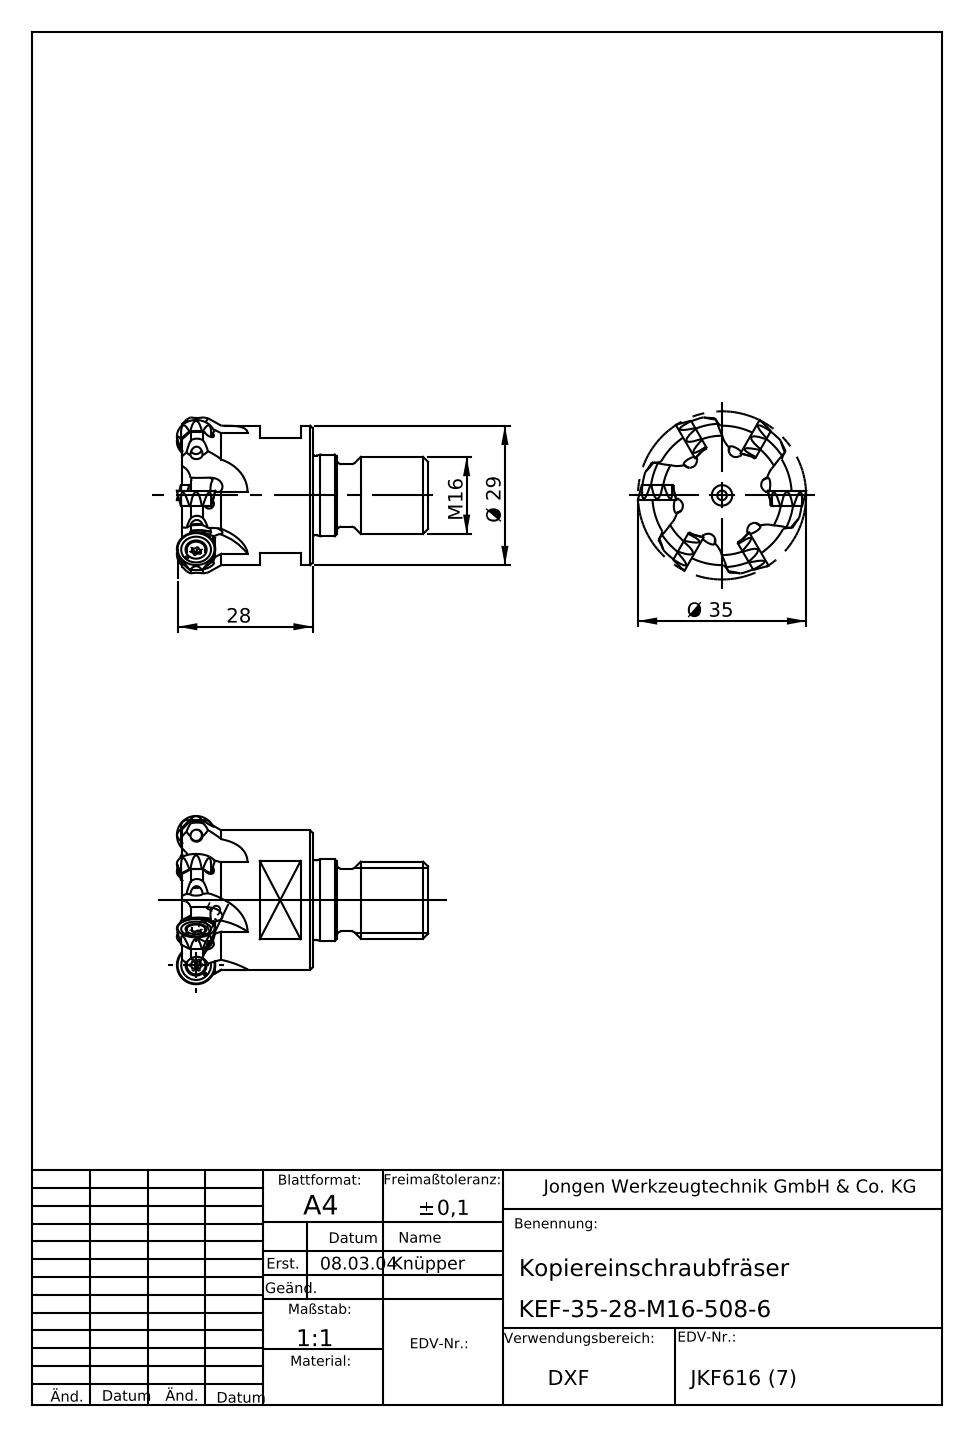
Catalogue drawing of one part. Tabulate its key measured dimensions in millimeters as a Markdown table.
| quantity | value |
| --- | --- |
| part name | KEF_35_28_M16_508_6 |
| STEP written by | SolidWorks 2016 (AUTOMOTIVE_DESIGN) |
| units | millimeters |
| bodies | 1 solid, 203 faces (79 planar, 58 cylindrical, 66 other) |
| overall size | 51.99 × 35 × 35 |
| volume | 21 753 mm³ |
| surface area | 7 269 mm² |
| round holes (diameter × count) | 3 × 6, 2 × 1, 4 × 1 |
| round bosses / shafts (diameter × count) | 29 × 1, 17 × 1, 16.6 × 1, 16 × 1, 13 × 1 |
| partial cylindrical surfaces (radius × count) | 1.5 × 12, 1 × 6 |
| main face-to-face distances | 24, 25.24, 49.24, 26.5, 35, 2.5, 11, 8.5, 22.74, 14.24 |
